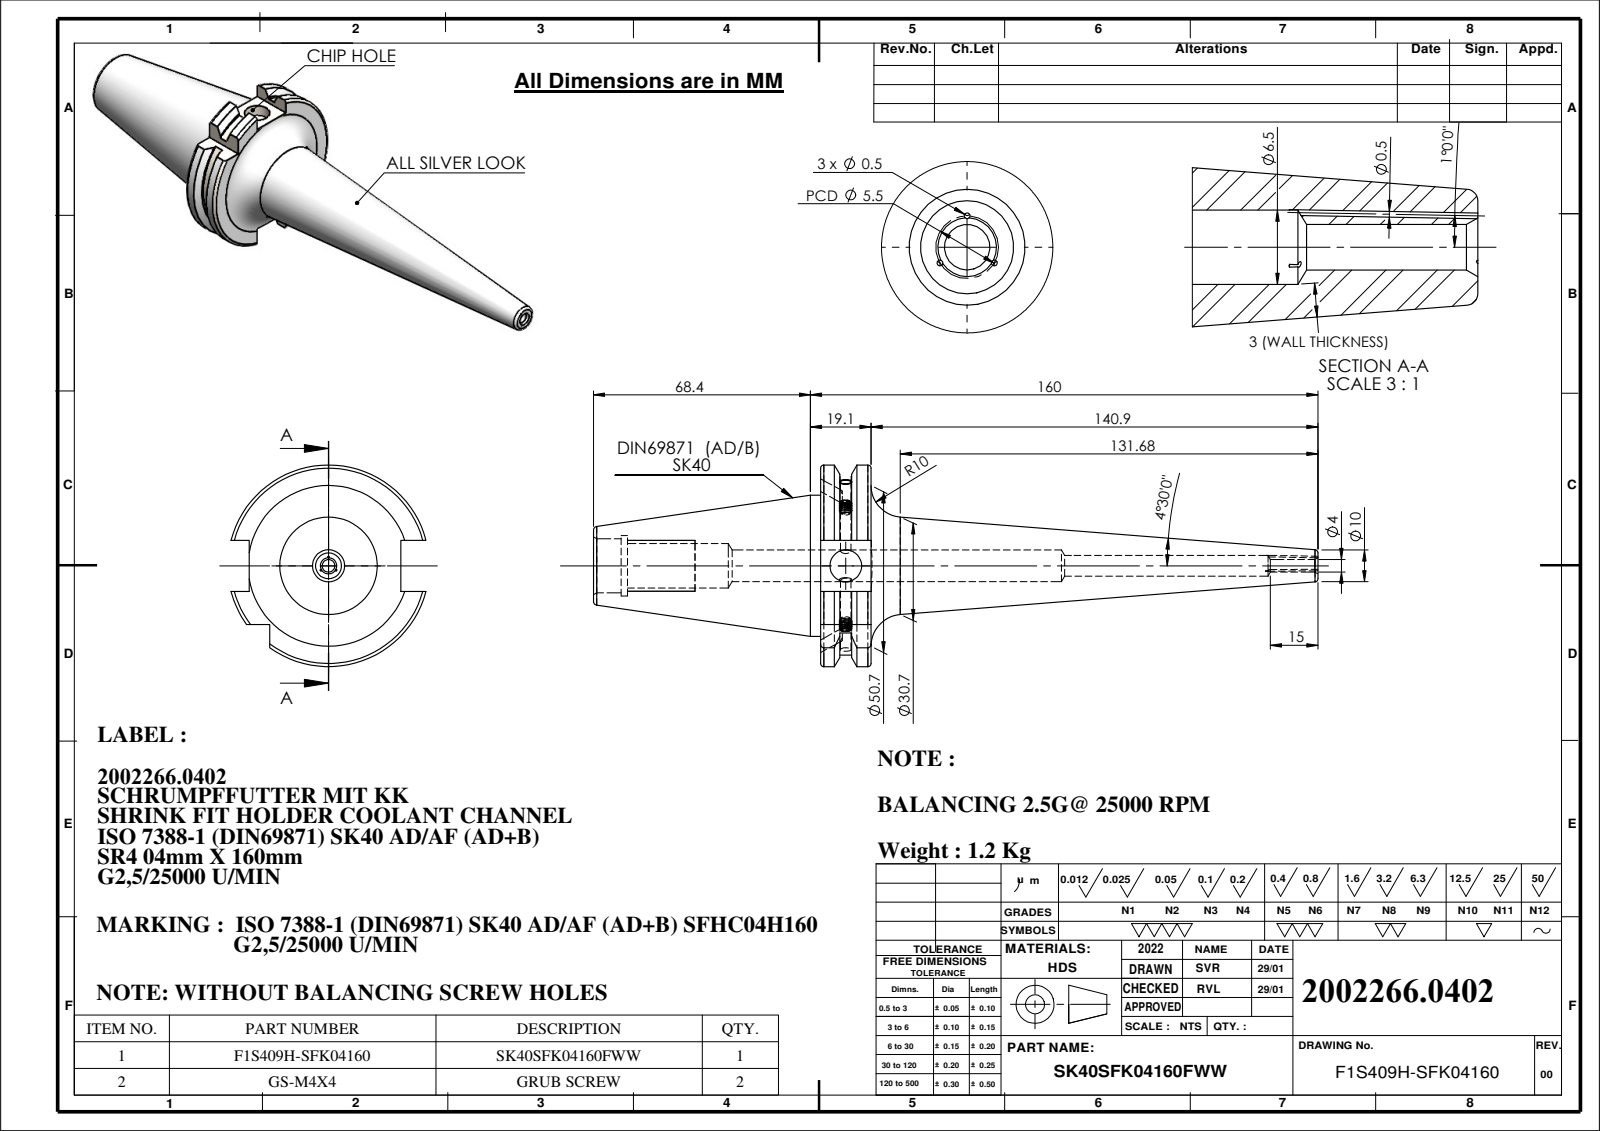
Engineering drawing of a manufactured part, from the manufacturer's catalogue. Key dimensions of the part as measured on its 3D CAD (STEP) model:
Part name (STEP PRODUCT): GS-M4X4_DIN 913 - M4 x 4-N; SK40SFK04160FWW; 91406-SR404160
STEP written by: SolidWorks 2018 (CONFIG_CONTROL_DESIGN)
Units: millimetres
Bodies: 3 solids, 207 faces (47 planar, 58 cylindrical, 102 other)
Overall size (bounding box): 228.4 × 63.55 × 61.48
Volume: 150 331 mm³ · Surface area: 32 952 mm²
Round holes (diameter × count): ⌀0.5 ×3, ⌀10 ×2, ⌀3.3 ×1, ⌀3.99 ×1, ⌀6.5 ×1, ⌀14 ×1, ⌀17 ×1, ⌀19 ×1
Round bosses / shafts (diameter × count): ⌀4 ×2, ⌀44.45 ×1
Partial cylindrical surfaces — rounded edges, fillets, slot ends (radius × count): R28.12 ×1, R31.77 ×1
Main face-to-face distances: 15.9, 16.1, 47.8, 71.6, 87.5, 10.7, 60.9, 76.8, 77.62, 66.92
